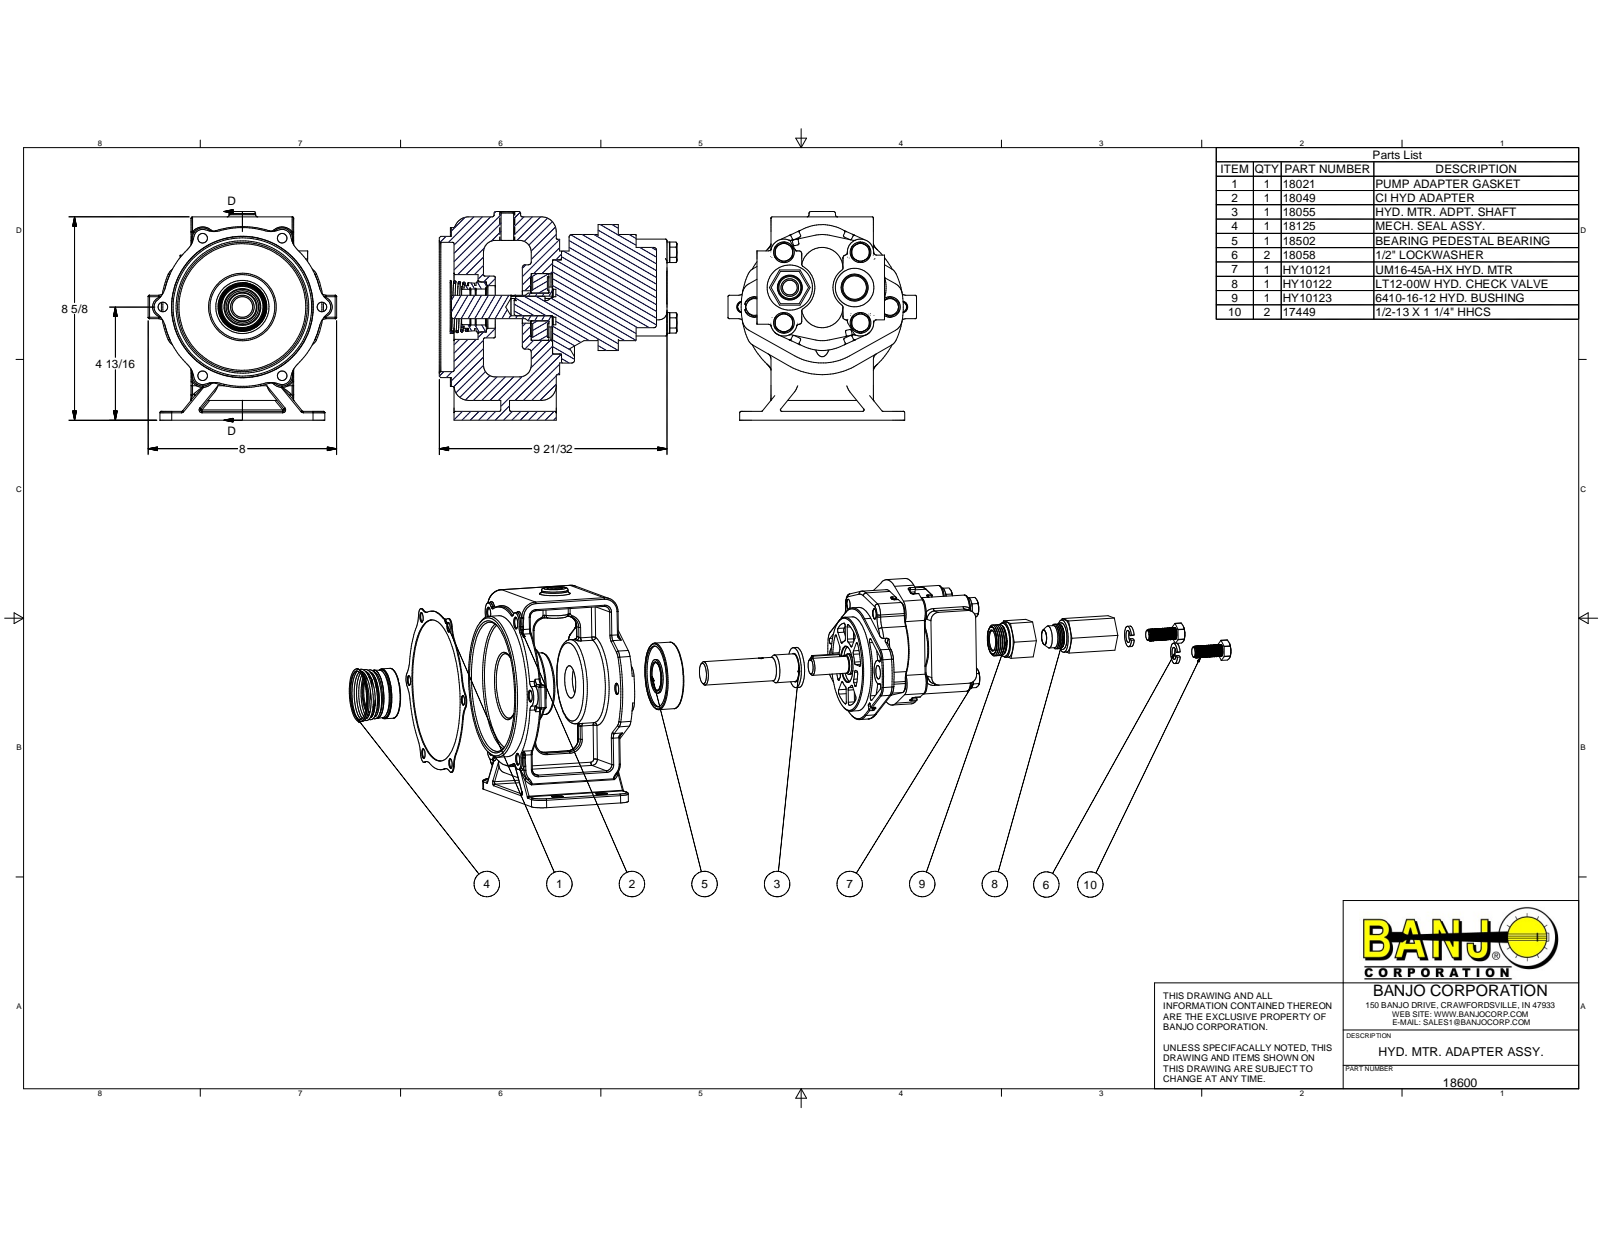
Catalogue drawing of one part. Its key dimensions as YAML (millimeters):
part_name: "18049; 18021; 18055; 18125 (+7 more)"
step_written_by: "Autodesk Inventor 2015 (AUTOMOTIVE_DESIGN)"
units: millimeters
bodies: {solids: 12, faces: 1911, planar: 420, cylindrical: 744, other: 747}
overall_size: [329.31, 225.3, 203.2]
volume: 2786000
surface_area: 508289
round_holes:
  - {diameter: 11.11, count: 14}
  - {diameter: 10.32, count: 6}
  - {diameter: 13.11, count: 4}
  - {diameter: 14.22, count: 4}
  - {diameter: 15.89, count: 4}
  - {diameter: 10.59, count: 2}
  - {diameter: 13, count: 2}
  - {diameter: 14.53, count: 2}
  - {diameter: 4.78, count: 1}
  - {diameter: 13.39, count: 1}
  - {diameter: 15.88, count: 1}
  - {diameter: 19.05, count: 1}
round_bosses_or_shafts:
  - {diameter: 11.07, count: 30}
  - {diameter: 12.7, count: 6}
  - {diameter: 22.22, count: 4}
  - {diameter: 18.54, count: 4}
  - {diameter: 22.07, count: 2}
  - {diameter: 152.4, count: 1}
  - {diameter: 101.57, count: 1}
  - {diameter: 91.05, count: 1}
partial_cylinders:
  - {radius: 1.52, count: 105}
  - {radius: 3.05, count: 84}
  - {radius: 1.59, count: 30}
  - {radius: 6.35, count: 28}
  - {radius: 3.17, count: 20}
  - {radius: 12.7, count: 18}
  - {radius: 0.76, count: 16}
  - {radius: 1.27, count: 16}
face_to_face_distances: [9.53, 9.52, 106.35, 209.93, 91.11, 100.64, 12.7, 103.81, 3.17, 15.24]
hole_center_spacings: [85.72, 148.48, 85.73, 38.63, 80.13, 85.19, 137.63, 171.45]
